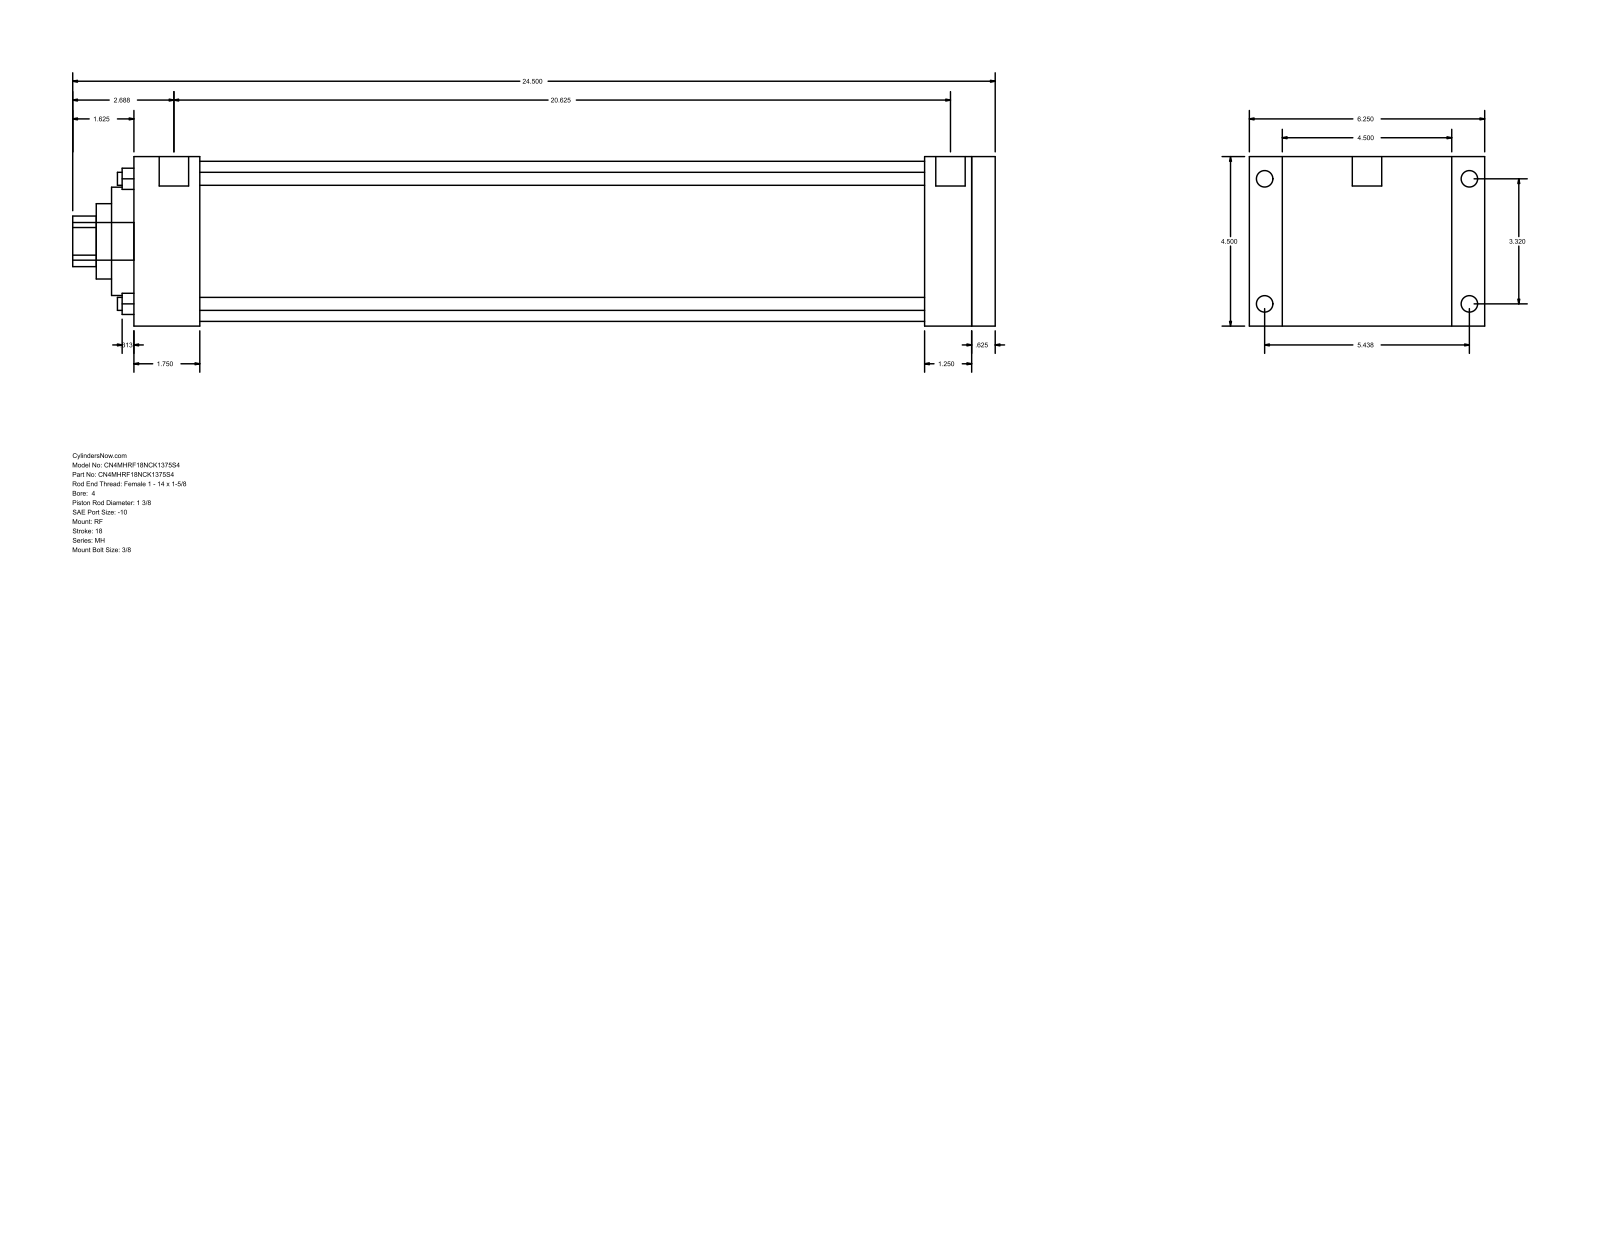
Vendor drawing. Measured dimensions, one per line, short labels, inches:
name: MH_RF__0400_1.375
written by: GSSL Pune (CONFIG_CONTROL_DESIGN)
unit: in
bodies: 0 solids, 94 faces (65 planar, 29 cylindrical, 0 other)
size: 24.5 × 6.25 × 4.5
holes: 4× ⌀0.345, 1× ⌀1.375, 1× ⌀2, 1× ⌀2.875, 1× ⌀4.25
bosses: 4× ⌀0.438, 4× ⌀0.344, 2× ⌀0.781, 1× ⌀1
rounds: 1× R0.672
face distances: 4.5, 22.875, 0.625, 22.25, 1.75, 20.5, 21.125, 21, 19.25, 1.25
hole spacings: 2.347, 3.32, 4.695
